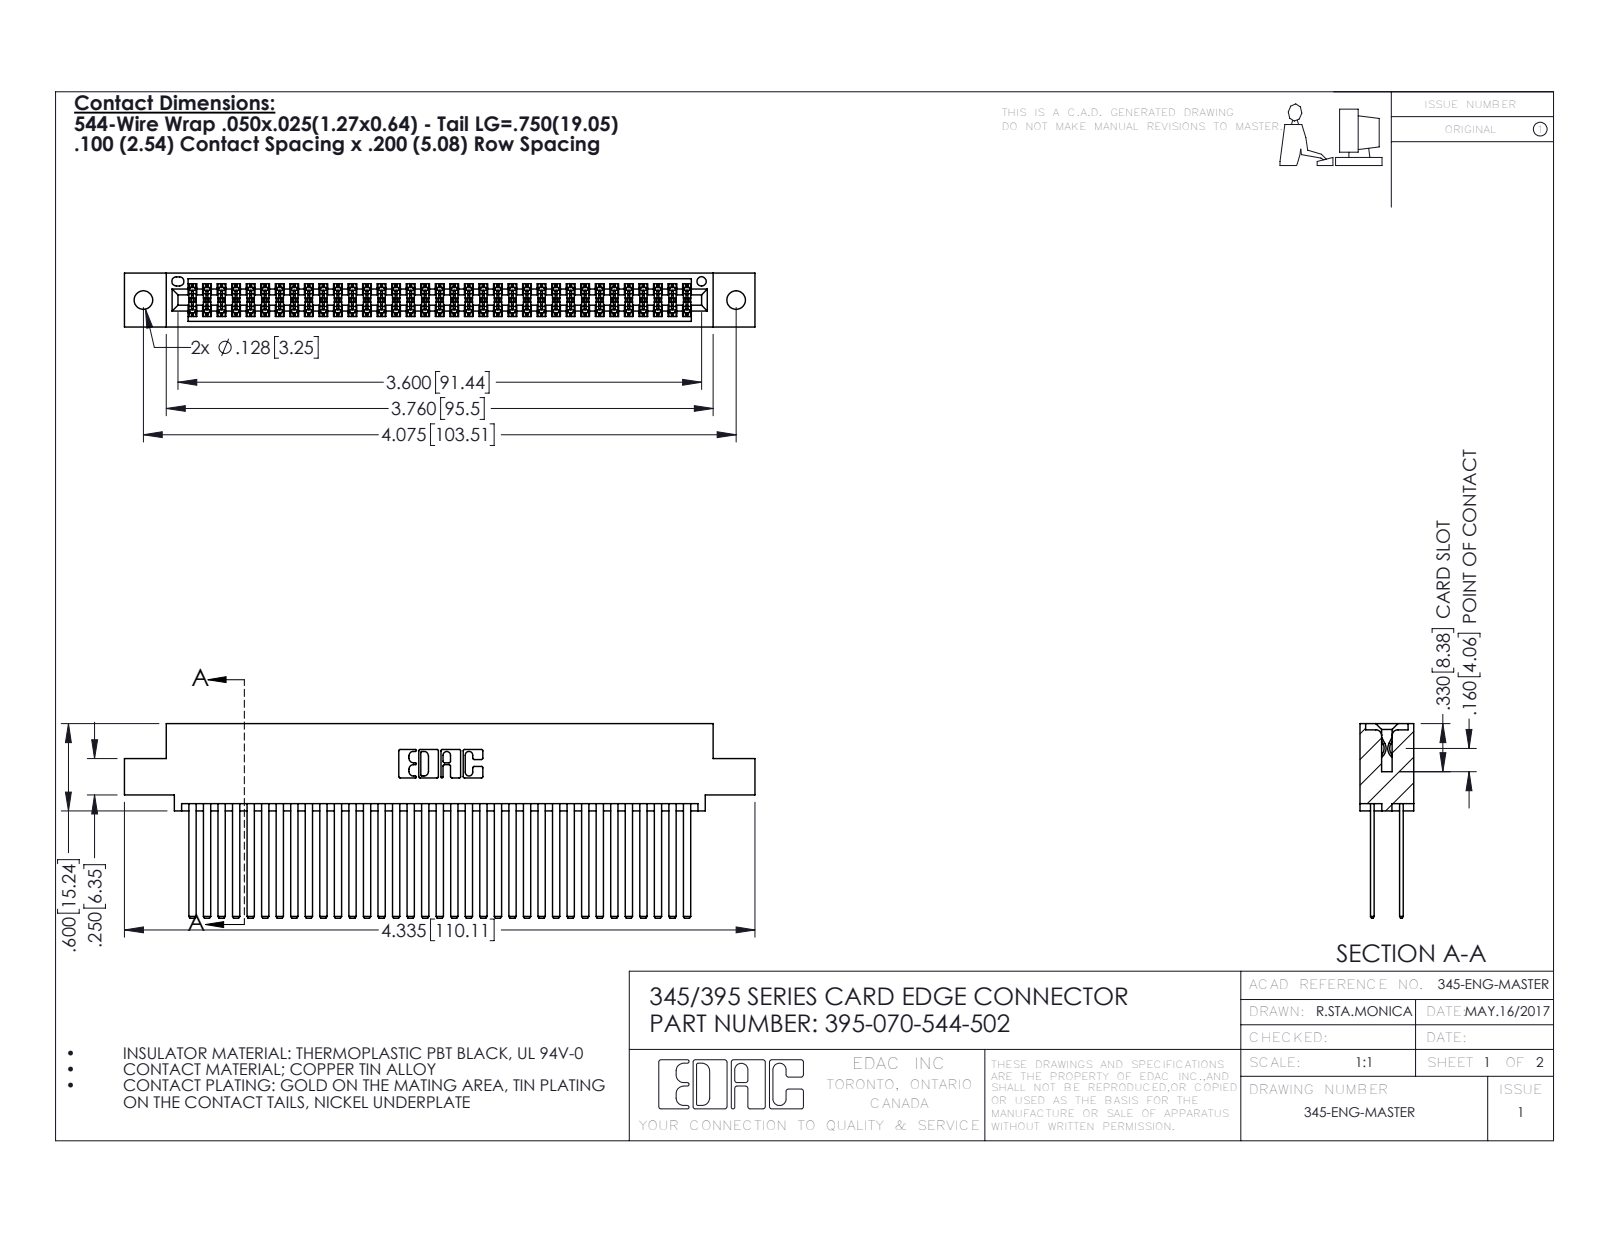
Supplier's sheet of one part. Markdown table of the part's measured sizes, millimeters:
| quantity | value |
| --- | --- |
| part name | 395-070-544-502; 345 Part_0.110 Offset - 0.128 Dia; 345-292-001_345-293-144 |
| STEP written by | SolidWorks 2016 (CONFIG_CONTROL_DESIGN) |
| units | millimeters |
| bodies | 71 solids, 3210 faces (2114 planar, 1096 cylindrical, 0 other) |
| overall size | 110.1 × 34 × 9.4 |
| volume | 11 500 mm³ |
| surface area | 19 560 mm² |
| round holes (diameter × count) | 3.3 × 2, 1.6 × 1 |
| partial cylindrical surfaces (radius × count) | 0.2 × 105, 0.3 × 22, 0.2 × 6, 0.8 × 6, 0.7 × 3, 0.4 × 2, 0.5 × 2, 0.6 × 2 |
| main face-to-face distances | 5.1, 0.6, 7.6, 1.8, 2.5, 6.9, 5.7, 4.4, 9.4, 1.3 |
| hole center spacings | 6.9, 97.5, 103.5 |
